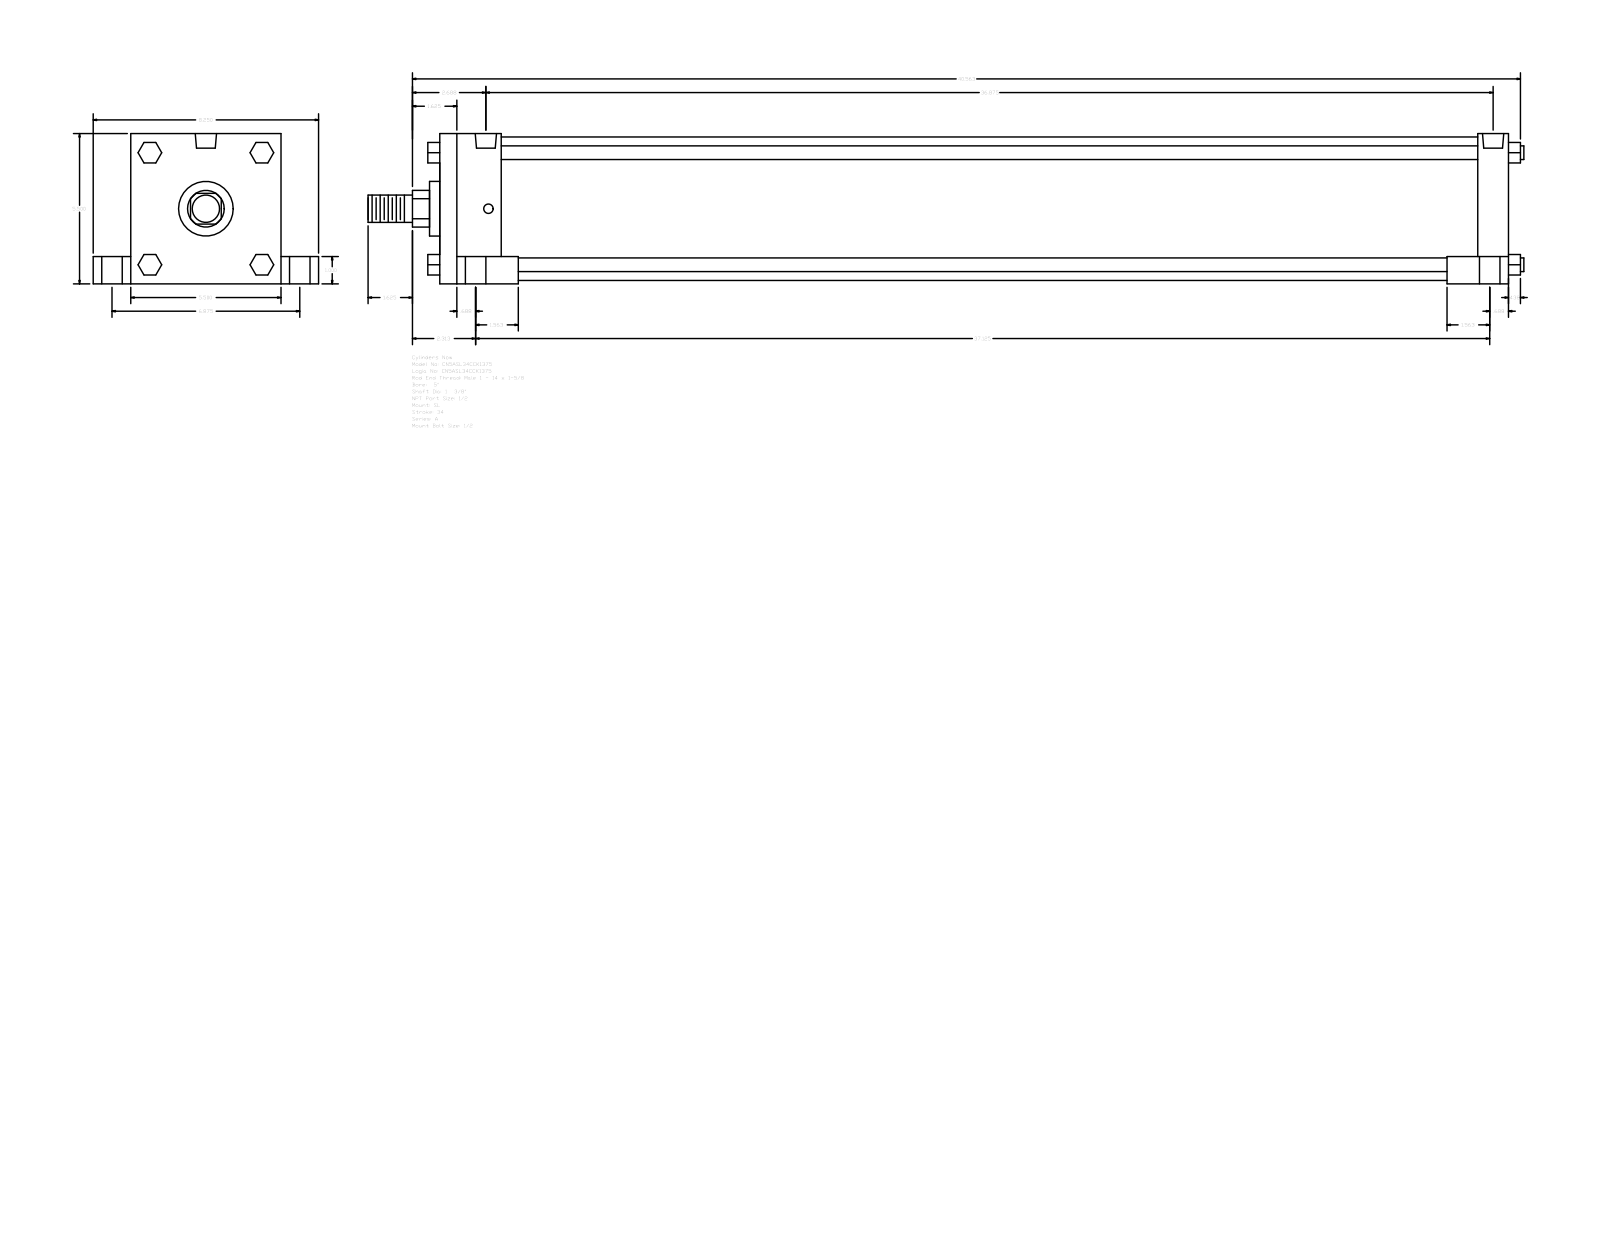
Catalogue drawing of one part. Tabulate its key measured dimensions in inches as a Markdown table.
| quantity | value |
| --- | --- |
| part name | A_SL__0500_1.375 |
| STEP written by | GSSL Pune (CONFIG_CONTROL_DESIGN) |
| units | inches |
| bodies | 0 solids, 150 faces (114 planar, 36 cylindrical, 0 other) |
| overall size | 42.313 × 8.25 × 5.5 |
| round holes (diameter × count) | 0.344 × 4, 0.75 × 4, 1 × 4, 0.778 × 2 |
| round bosses / shafts (diameter × count) | 0.5 × 4, 5.25 × 1, 2 × 1, 1.375 × 1, 1 × 1 |
| partial cylindrical surfaces (radius × count) | 0.672 × 1 |
| main face-to-face distances | 5.5, 39.125, 2.25, 36.875, 1, 4.5, 1.375, 6.875, 1.125, 38 |
| hole center spacings | 0.094, 3.437, 3.44, 3.458, 3.469, 6.875, 36.687, 36.781 |
